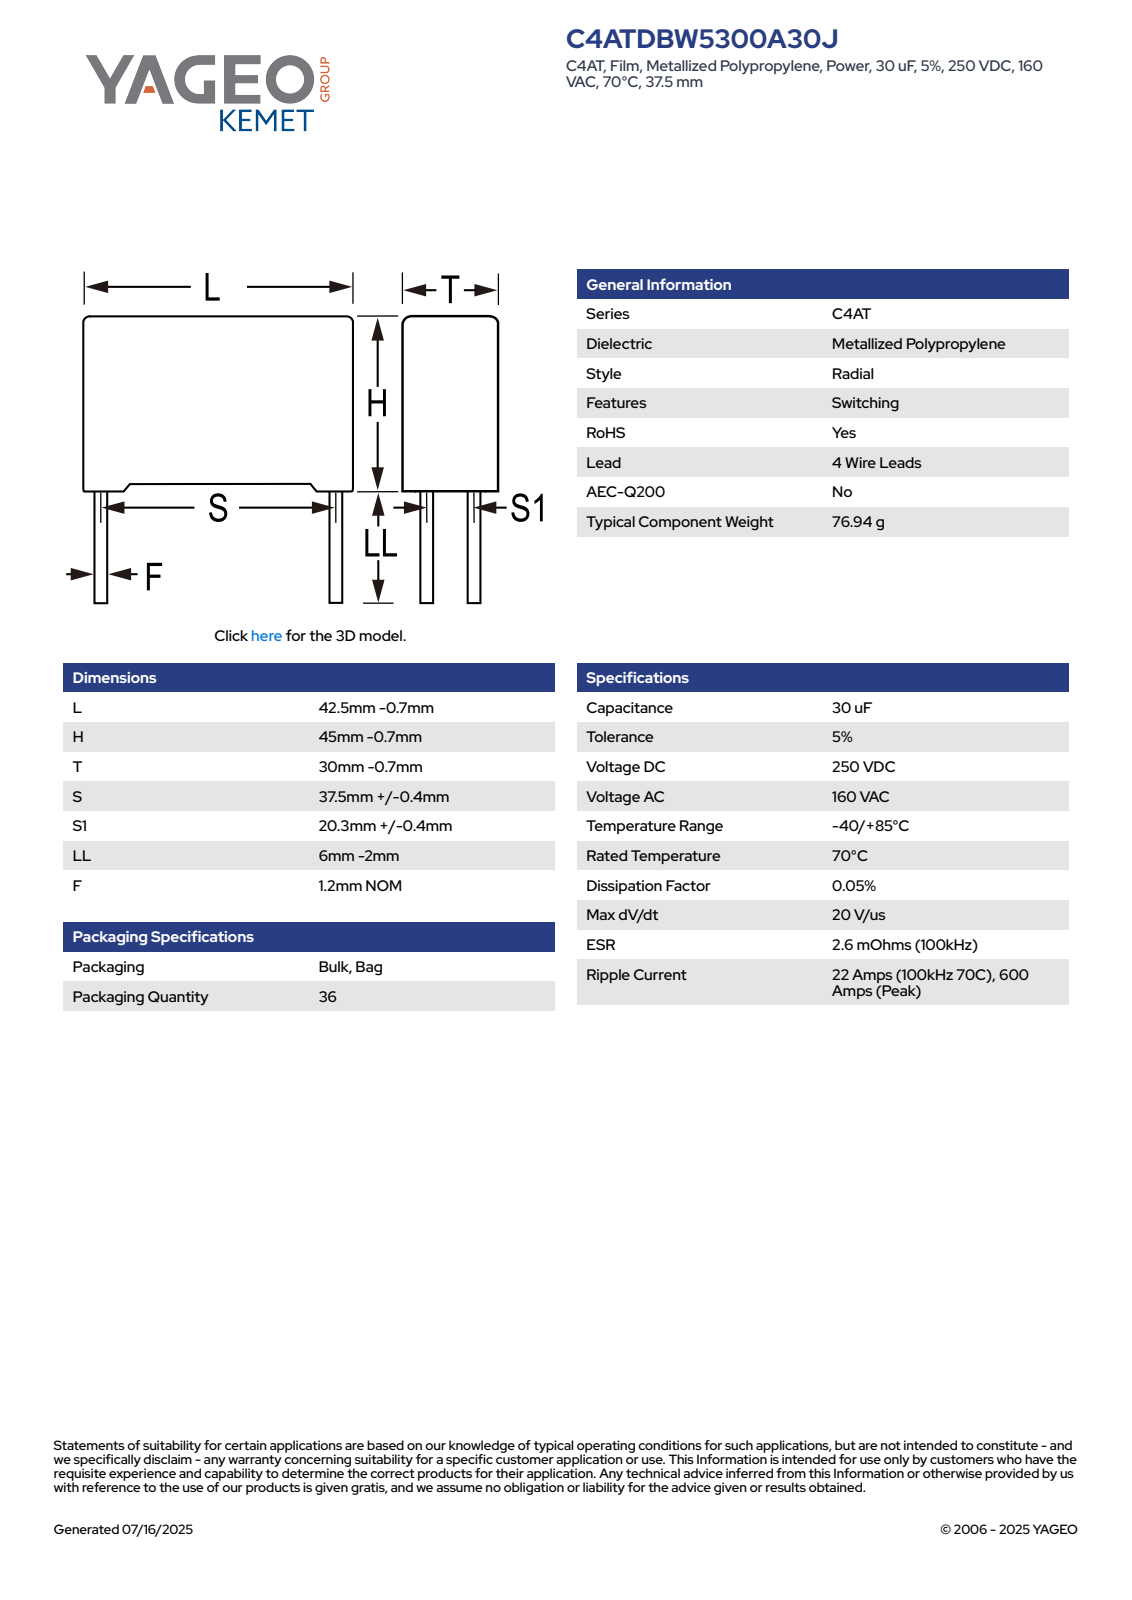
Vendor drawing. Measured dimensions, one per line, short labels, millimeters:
name: CFP_RB4_42.5X45X30_L41.8H44.3T29.3S37.5S120.3LL4F1.2
written by: SolidWorks 2014 (AUTOMOTIVE_DESIGN)
unit: mm
bodies: 4 solids, 91 faces (83 planar, 8 cylindrical, 0 other)
size: 48.3 × 41.8 × 29.3
volume: 52 870 mm³; area: 8 957 mm²
bosses: 4× ⌀1.2
face distances: 29.3, 41.8, 43, 1.3, 44.3, 1.8, 40, 38.2, 27.5, 25.7
